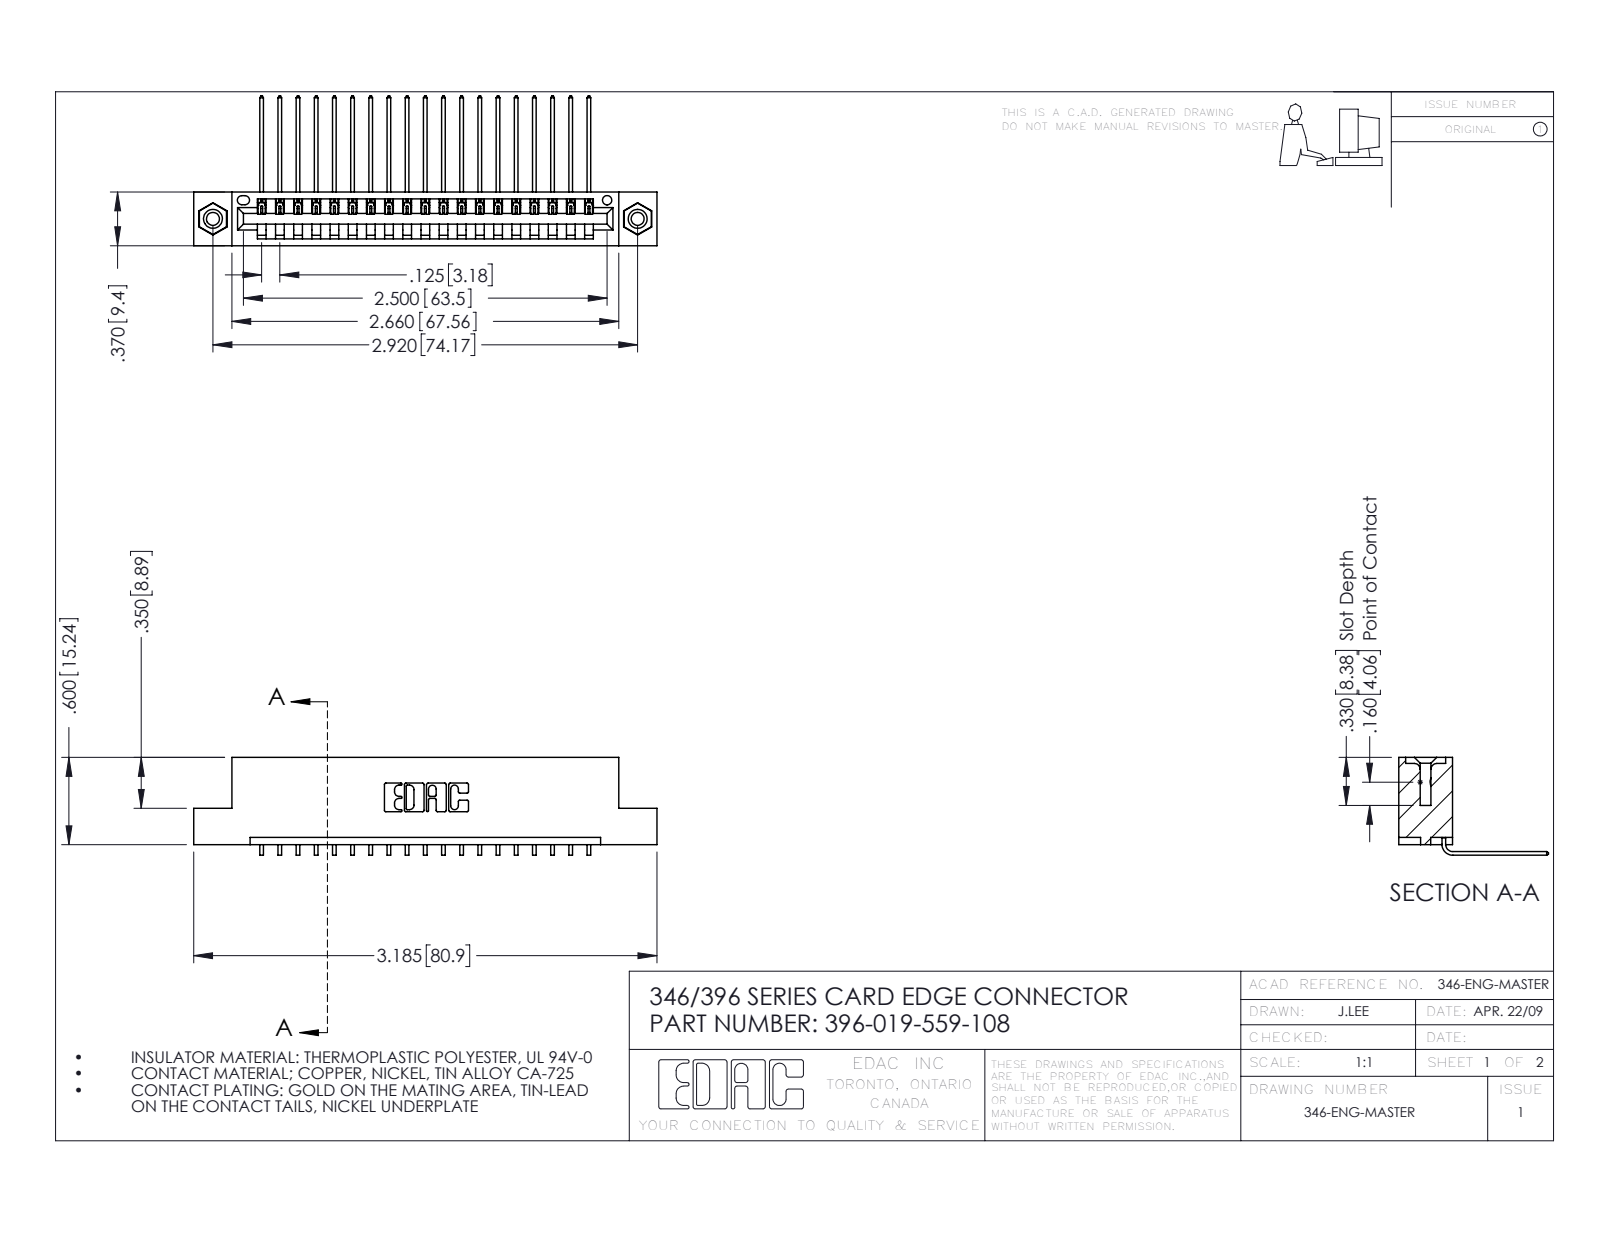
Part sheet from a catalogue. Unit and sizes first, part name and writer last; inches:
Units: inches
Overall size (bounding box): 3.185 × 1.03 × 0.673
Round holes (diameter × count): ⌀0.089 ×2, ⌀0.125 ×2, ⌀0.156 ×2, ⌀0.064 ×1
Round bosses / shafts (diameter × count): ⌀0.155 ×2
Partial cylindrical surfaces — rounded edges, fillets, slot ends (radius × count): R0.006 ×38, R0.01 ×22, R0.007 ×6, R0.031 ×6, R0.026 ×3, R0.031 ×2, R0.04 ×2, R0.014 ×1
Main face-to-face distances: 0.048, 0.322, 0.37, 0.25, 0.072, 0.025, 0.298, 0.148, 0.222, 0.1
Hole centre spacings: 0.246, 2.713, 2.92
Volume: 0.466 in³ · Surface area: 15.04 in²
Bodies: 22 solids, 1322 faces (906 planar, 400 cylindrical, 16 other)
Part name (STEP PRODUCT): 396-019-559-108; 345-250-001_345-250-003-102; 346 Part_Flush Mounting Lugs - 0.156 Dia-TI; 345-292-001_558 559 Tail - 1
STEP written by: SolidWorks 2016 (CONFIG_CONTROL_DESIGN)
